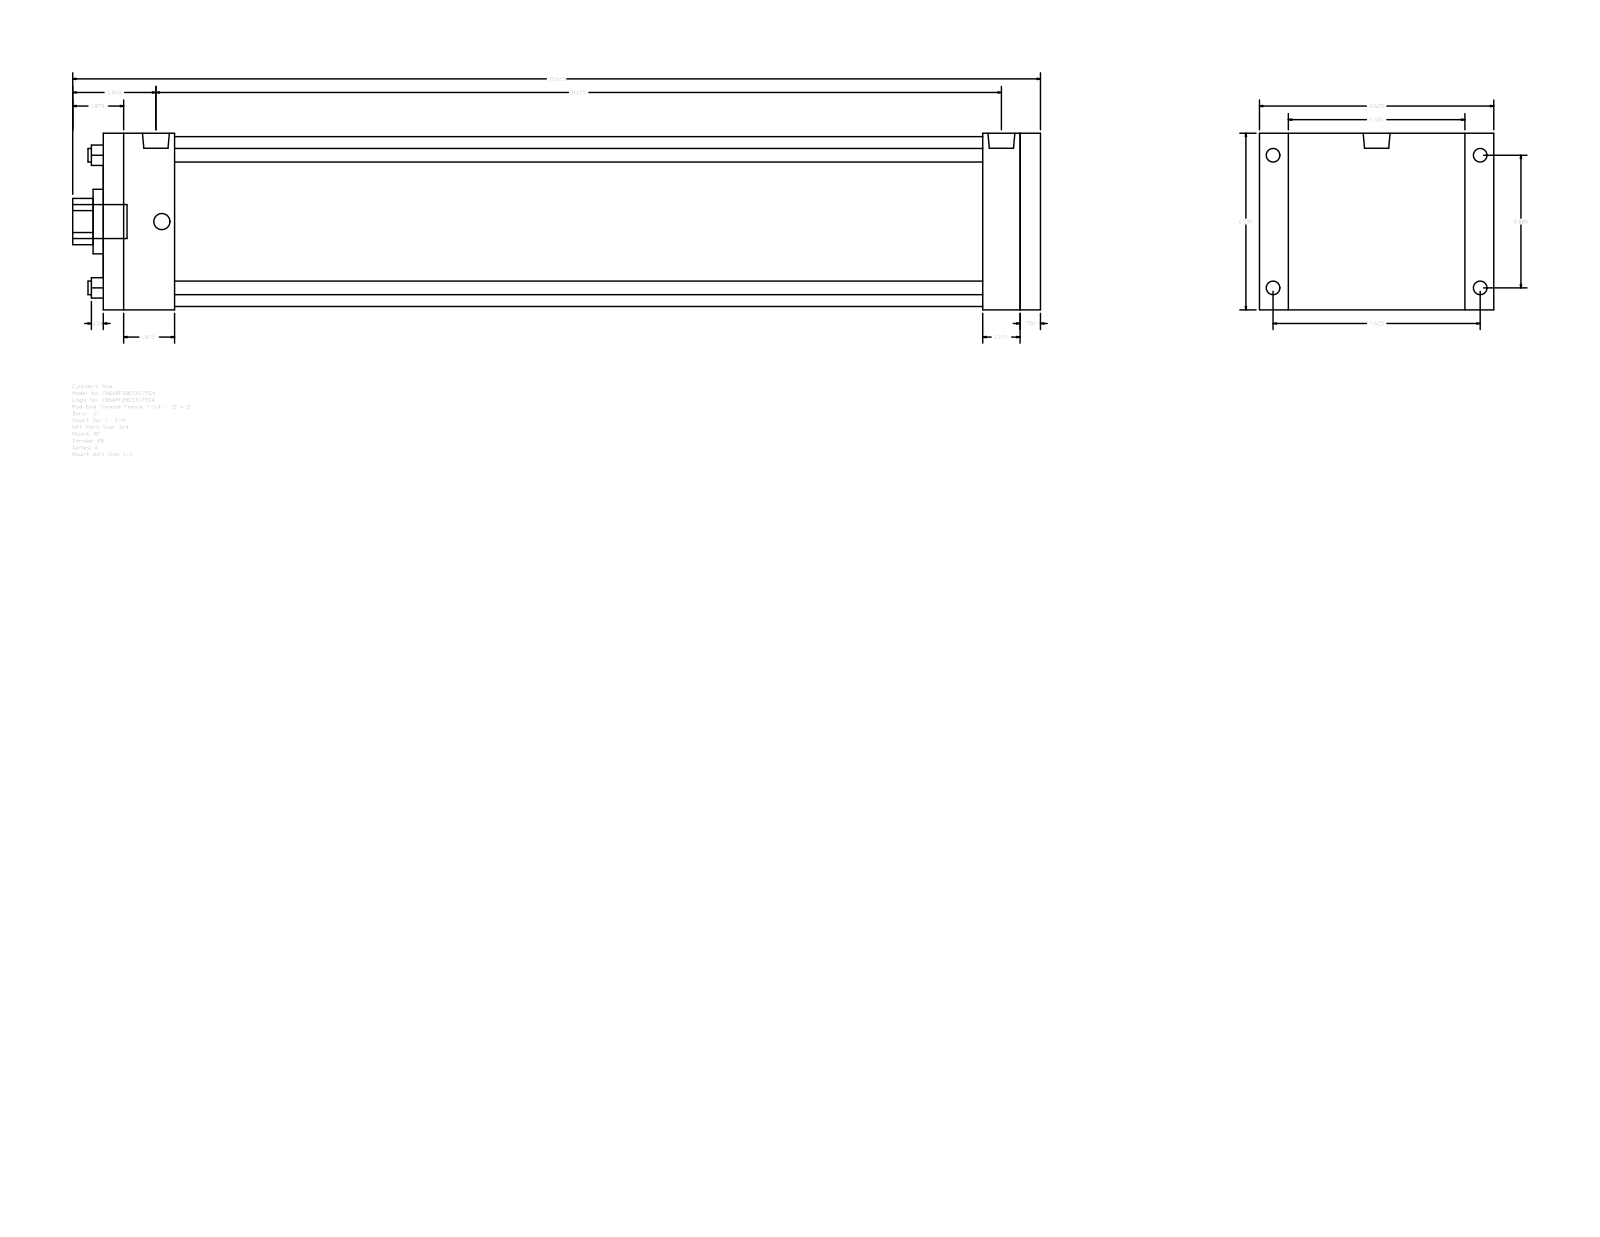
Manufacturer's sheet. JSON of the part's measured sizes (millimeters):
{"part_name": "A_RF__0600_1.75", "step_written_by": "GSSL Pune (CONFIG_CONTROL_DESIGN)", "units": "millimeters", "bodies": {"solids": 0, "faces": 92, "planar": 64, "cylindrical": 28, "other": 0}, "overall_size": [904.88, 219.07, 165.1], "round_holes": [[12.7, 4], [44.45, 1], [60.33, 1], [158.75, 1]], "round_bosses_or_shafts": [[15.08, 4], [12.7, 4], [25.12, 2], [31.75, 1]], "partial_cylinders_radius": [[21.63, 1]], "face_to_face_distances": [165.1, 876.31, 19.05, 857.26, 66.68, 790.58, 809.63, 822.33, 755.65, 34.93], "hole_center_spacings": [87.65, 123.96, 175.31]}
